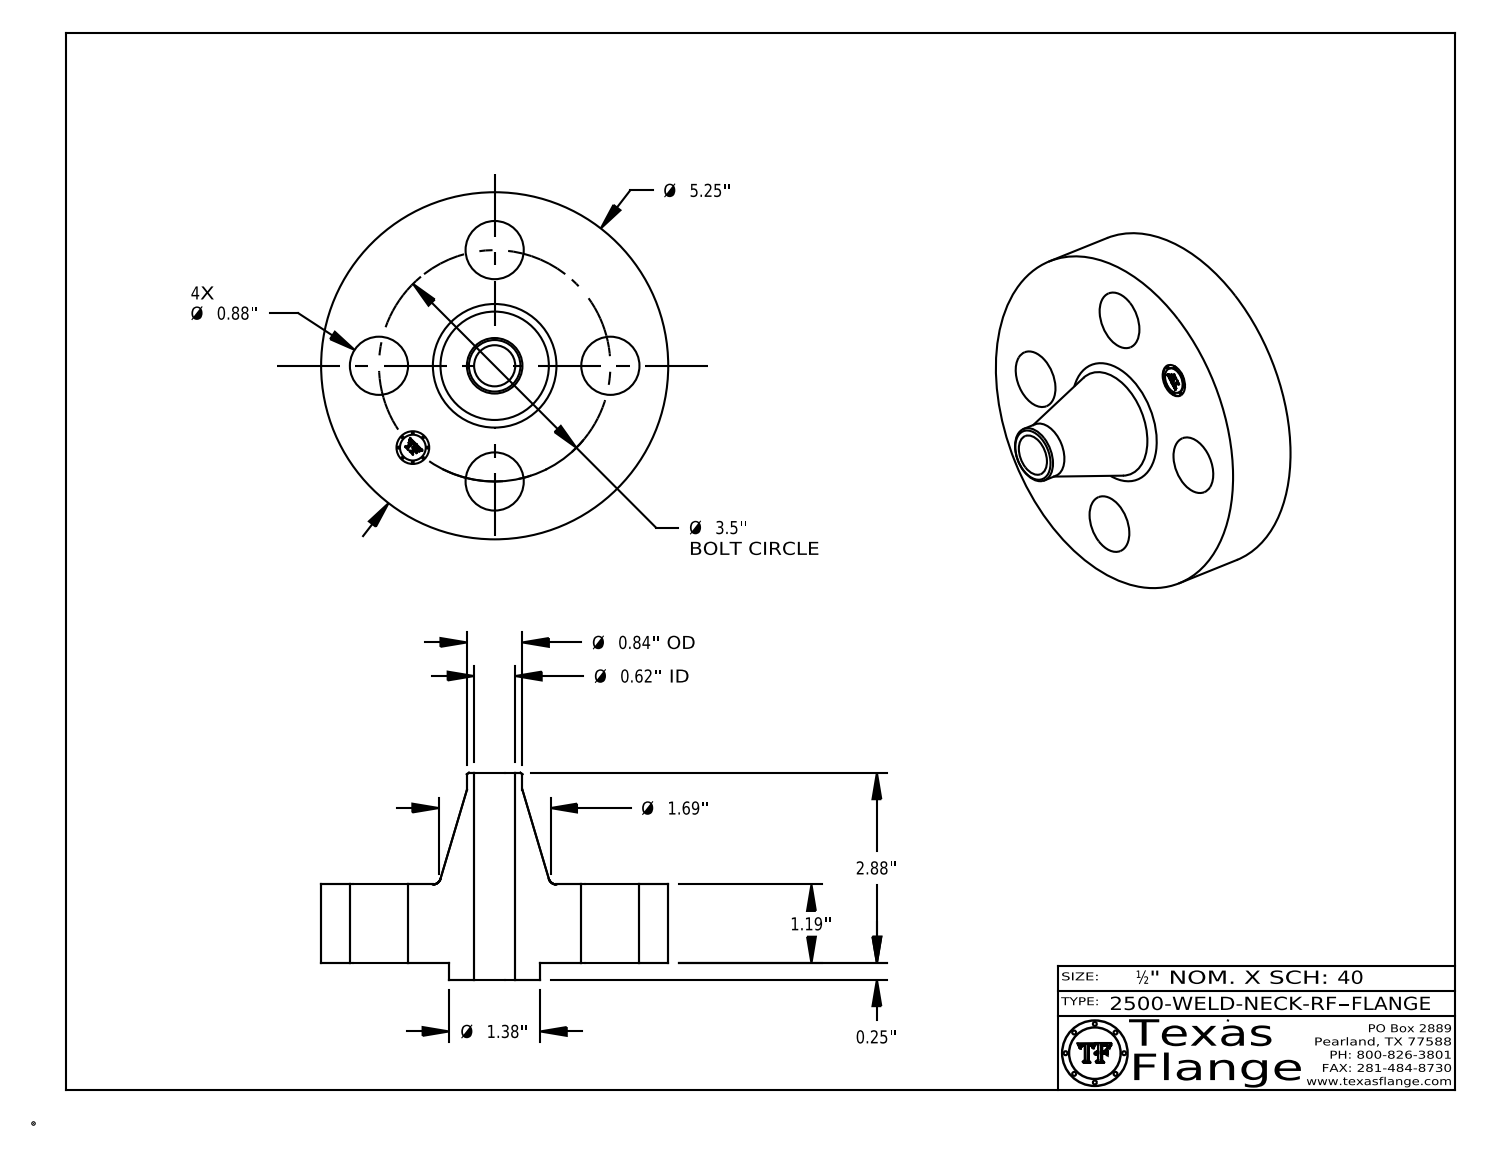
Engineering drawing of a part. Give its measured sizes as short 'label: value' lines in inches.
name: 2500-WELD-NECK-RF
written by: CATIA V5 STEP AP214 (AUTOMOTIVE_DESIGN)
unit: in
bodies: 1 solid, 411 faces (369 planar, 36 cylindrical, 6 other)
size: 5.25 × 5.25 × 3.13
volume: 24.3 in³; area: 82.66 in²
holes: 4× ⌀0.88, 1× ⌀0.495, 1× ⌀0.622
bosses: 8× ⌀0.03, 1× ⌀5.25, 1× ⌀1.38, 1× ⌀0.84, 1× ⌀0.39
face distances: 1.19, 0.25, 1.44, 3.13, 2.88, 1.69, 1.425, 1.175, 0.015, 1.705
hole spacings: 1.75, 2.475, 1.339, 3.233, 3.5
